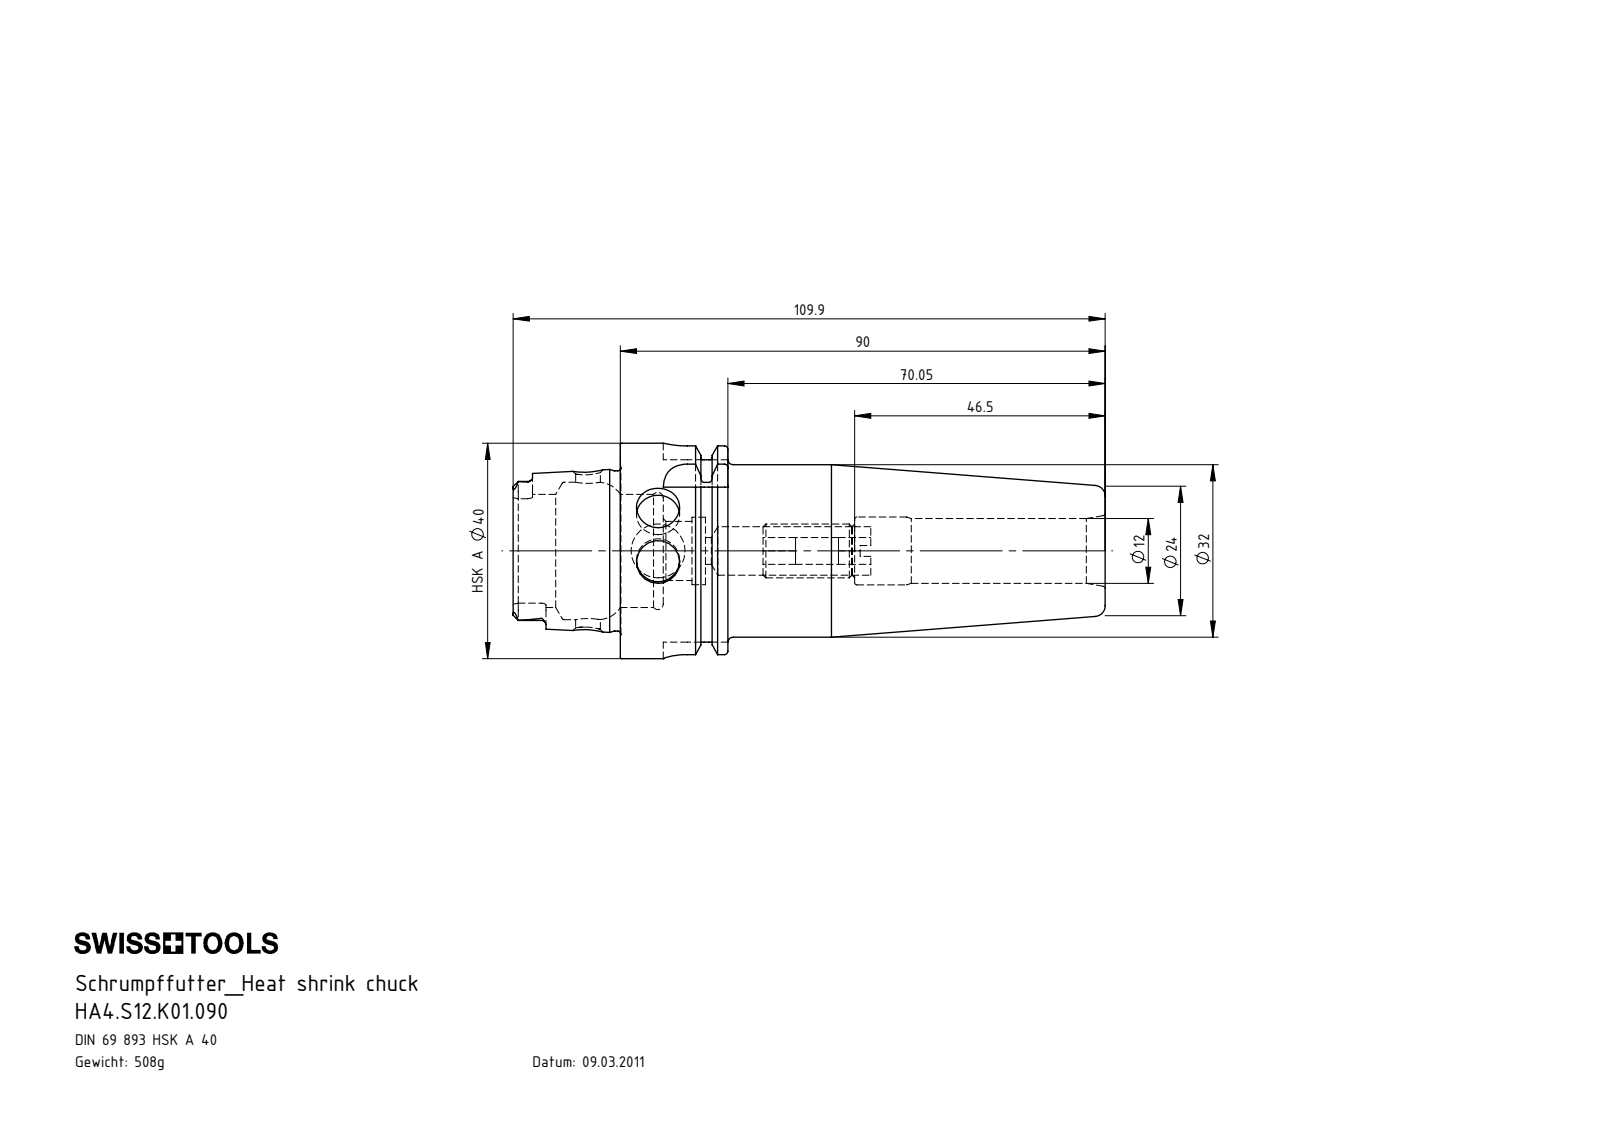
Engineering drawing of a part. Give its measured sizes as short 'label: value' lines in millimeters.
name: HA4-S12.K01.090_C_Fertigbearbeitung; ERU-AN4.K01.020_A; HA4-S12.K01.090
written by: SolidWorks 2015 (CONFIG_CONTROL_DESIGN)
unit: mm
bodies: 2 solids, 227 faces (82 planar, 62 cylindrical, 83 other)
size: 109.9 × 40 × 40
volume: 64 705 mm³; area: 19 162 mm²
holes: 2× ⌀8, 1× ⌀4.6, 1× ⌀5, 1× ⌀9, 1× ⌀10, 1× ⌀11, 1× ⌀12, 1× ⌀12.5, 1× ⌀12.6, 1× ⌀21, 1× ⌀25.5
bosses: 1× ⌀40, 1× ⌀34.75, 1× ⌀32, 1× ⌀29.71, 1× ⌀10
rounds: 6× R0.9, 4× R1.88, 4× R4.5
face distances: 19.95, 12, 7.95, 90, 82.05, 70.05, 19.9, 27.85, 39.85, 109.9
